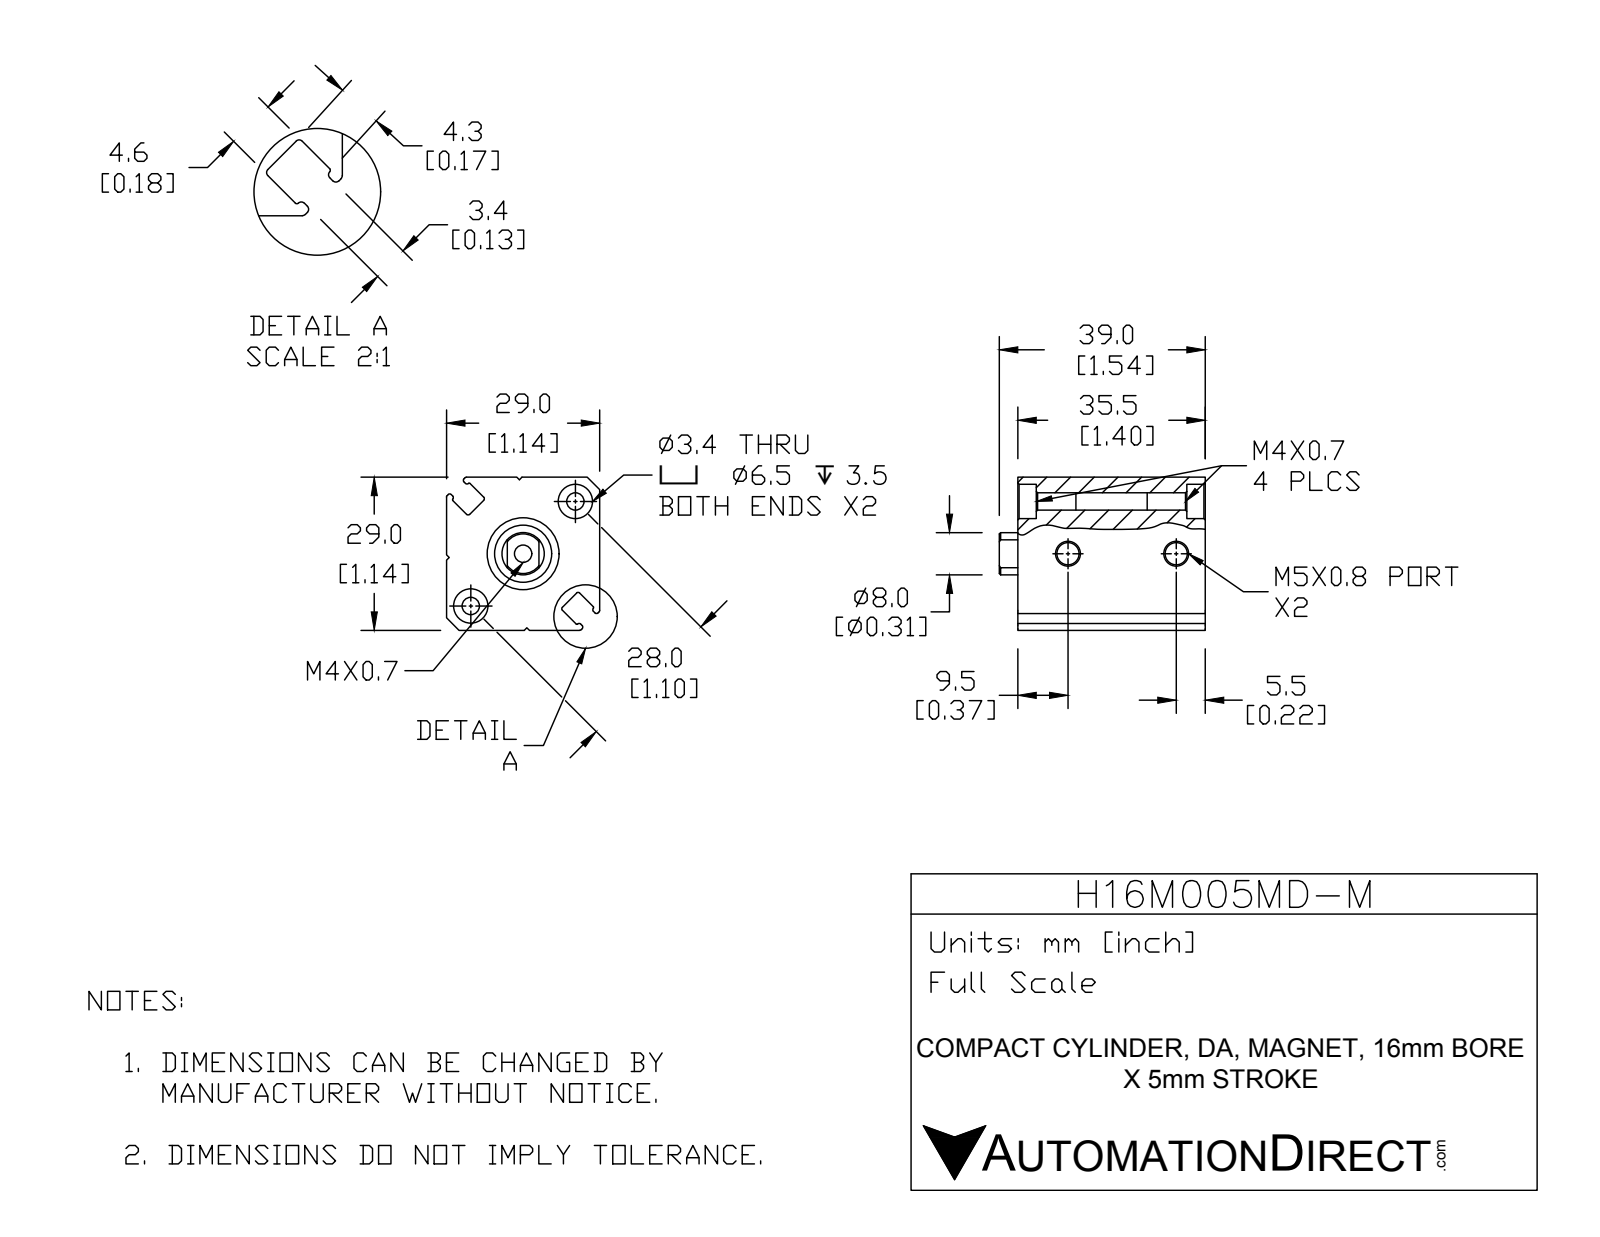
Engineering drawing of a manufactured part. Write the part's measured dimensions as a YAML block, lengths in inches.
part_name: "H16M005MD-M-BODY; H16M005MD-M-PISTON; H16M005MD-M"
step_written_by: "SolidWorks 2015 (CONFIG_CONTROL_DESIGN)"
units: inches
bodies: {solids: 2, faces: 128, planar: 49, cylindrical: 54, other: 25}
overall_size: [1.535, 1.142, 1.142]
volume: 1.546
surface_area: 16.84
round_holes:
  - {diameter: 0.13, count: 3}
  - {diameter: 0.165, count: 2}
  - {diameter: 0.256, count: 2}
  - {diameter: 0.315, count: 1}
  - {diameter: 0.535, count: 1}
  - {diameter: 0.63, count: 1}
round_bosses_or_shafts:
  - {diameter: 0.425, count: 1}
partial_cylinders:
  - {radius: 0.016, count: 16}
  - {radius: 0.008, count: 4}
face_to_face_distances: [1.142, 1.398, 0.157, 1.24, 0.181, 0.651, 0.832, 0.795, 0.638, 0.602]
hole_center_spacings: [0.551, 0.807, 1.102]
